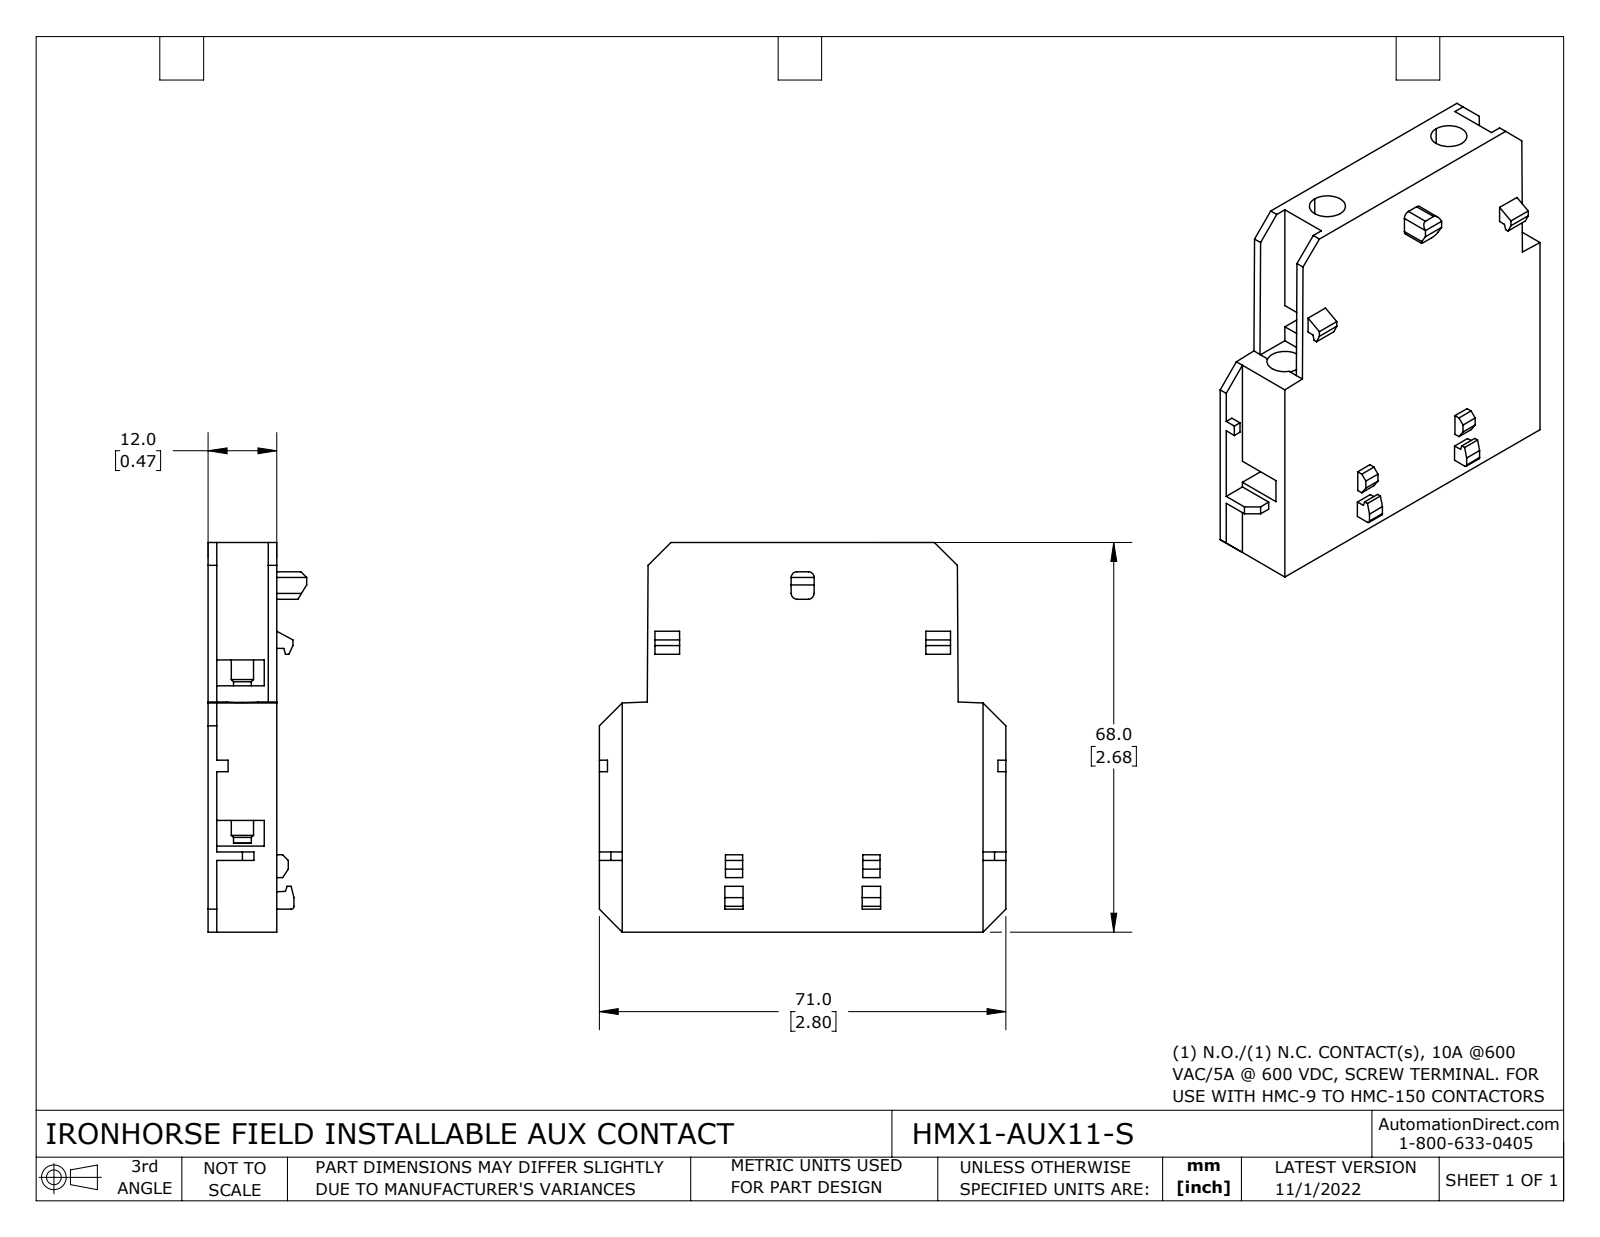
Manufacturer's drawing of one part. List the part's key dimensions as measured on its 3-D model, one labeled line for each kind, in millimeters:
Part name (STEP PRODUCT): HMX1-AUX11-S
STEP written by: SolidWorks 2021 (CONFIG_CONTROL_DESIGN)
Units: millimetres
Bodies: 5 solids, 209 faces (123 planar, 14 cylindrical, 72 other)
Overall size (bounding box): 71 × 68 × 17.2
Volume: 42 640 mm³ · Surface area: 15 960 mm²
Round holes (diameter × count): ⌀6.3 ×4
Partial cylindrical surfaces — rounded edges, fillets, slot ends (radius × count): R1 ×4, R0.5 ×1
Main face-to-face distances: 12, 10.5, 1.5, 52.5, 68, 63, 28, 9, 42, 4.5
Hole centre spacings: 10.5, 40.5, 30, 51
